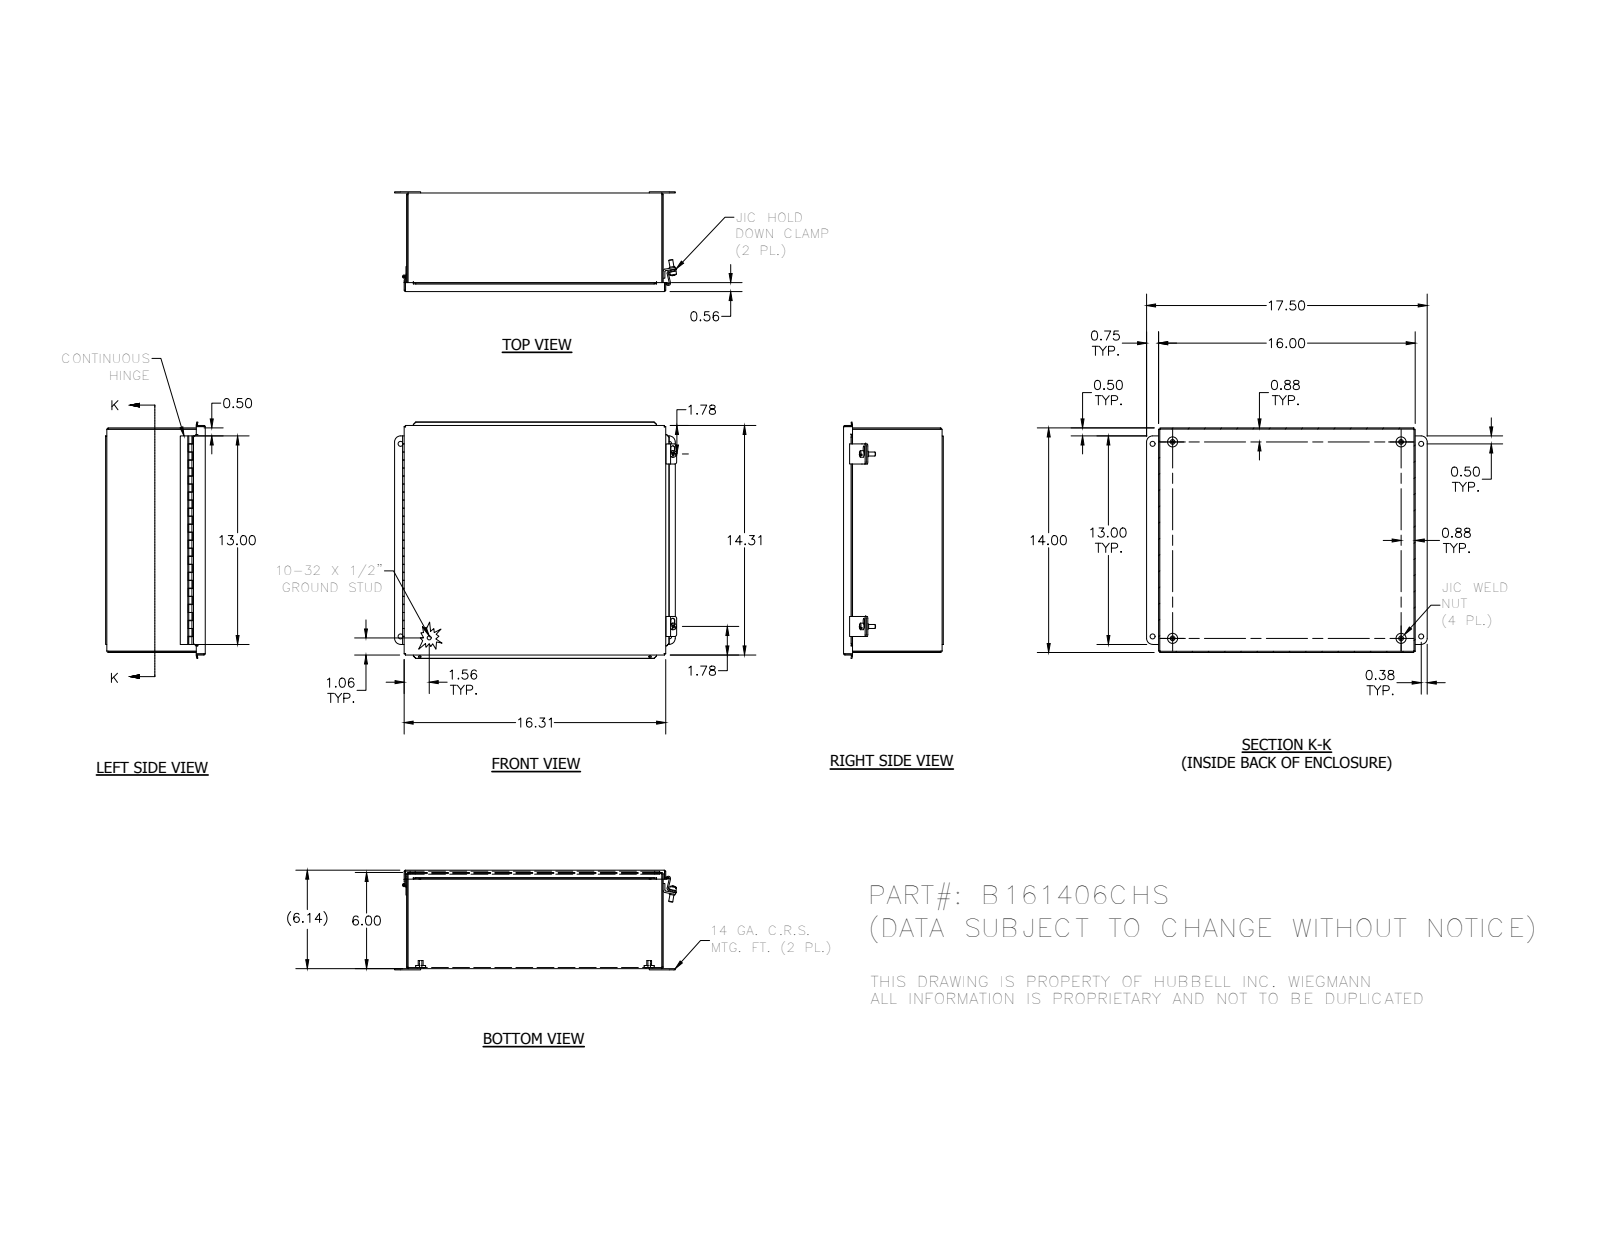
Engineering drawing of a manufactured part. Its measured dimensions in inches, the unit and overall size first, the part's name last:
Units: inches
Overall size (bounding box): 17.585 × 14.739 × 6.219
Round holes (diameter × count): ⌀0.156 ×4, ⌀0.31 ×4, ⌀0.14 ×2, ⌀0.196 ×2, ⌀0.116 ×1
Round bosses / shafts (diameter × count): ⌀0.625 ×4, ⌀0.3 ×4, ⌀0.25 ×3, ⌀0.41 ×2, ⌀0.344 ×2, ⌀0.2 ×1, ⌀0.19 ×1, ⌀0.1 ×1
Partial cylindrical surfaces — rounded edges, fillets, slot ends (radius × count): R0.031 ×15, R0.105 ×8, R0.125 ×8, R0.093 ×7, R0.133 ×4, R0.375 ×4, R0.063 ×3, R0.126 ×3
Main face-to-face distances: 0.074, 6.083, 0.062, 6.144, 6.009, 6.07, 13.926, 15.926, 14, 13.852
Hole centre spacings: 12.189, 1.256, 15.5, 19.679, 12, 12.25, 14.25, 18.792
Volume: 72.52 in³ · Surface area: 1 997 in²
Bodies: 20 solids, 519 faces (335 planar, 139 cylindrical, 45 other)
Part name (STEP PRODUCT): B161406CHS; 3499; 3486; C1001 (+8 more)
STEP written by: Autodesk Inventor 2012 (AUTOMOTIVE_DESIGN)
